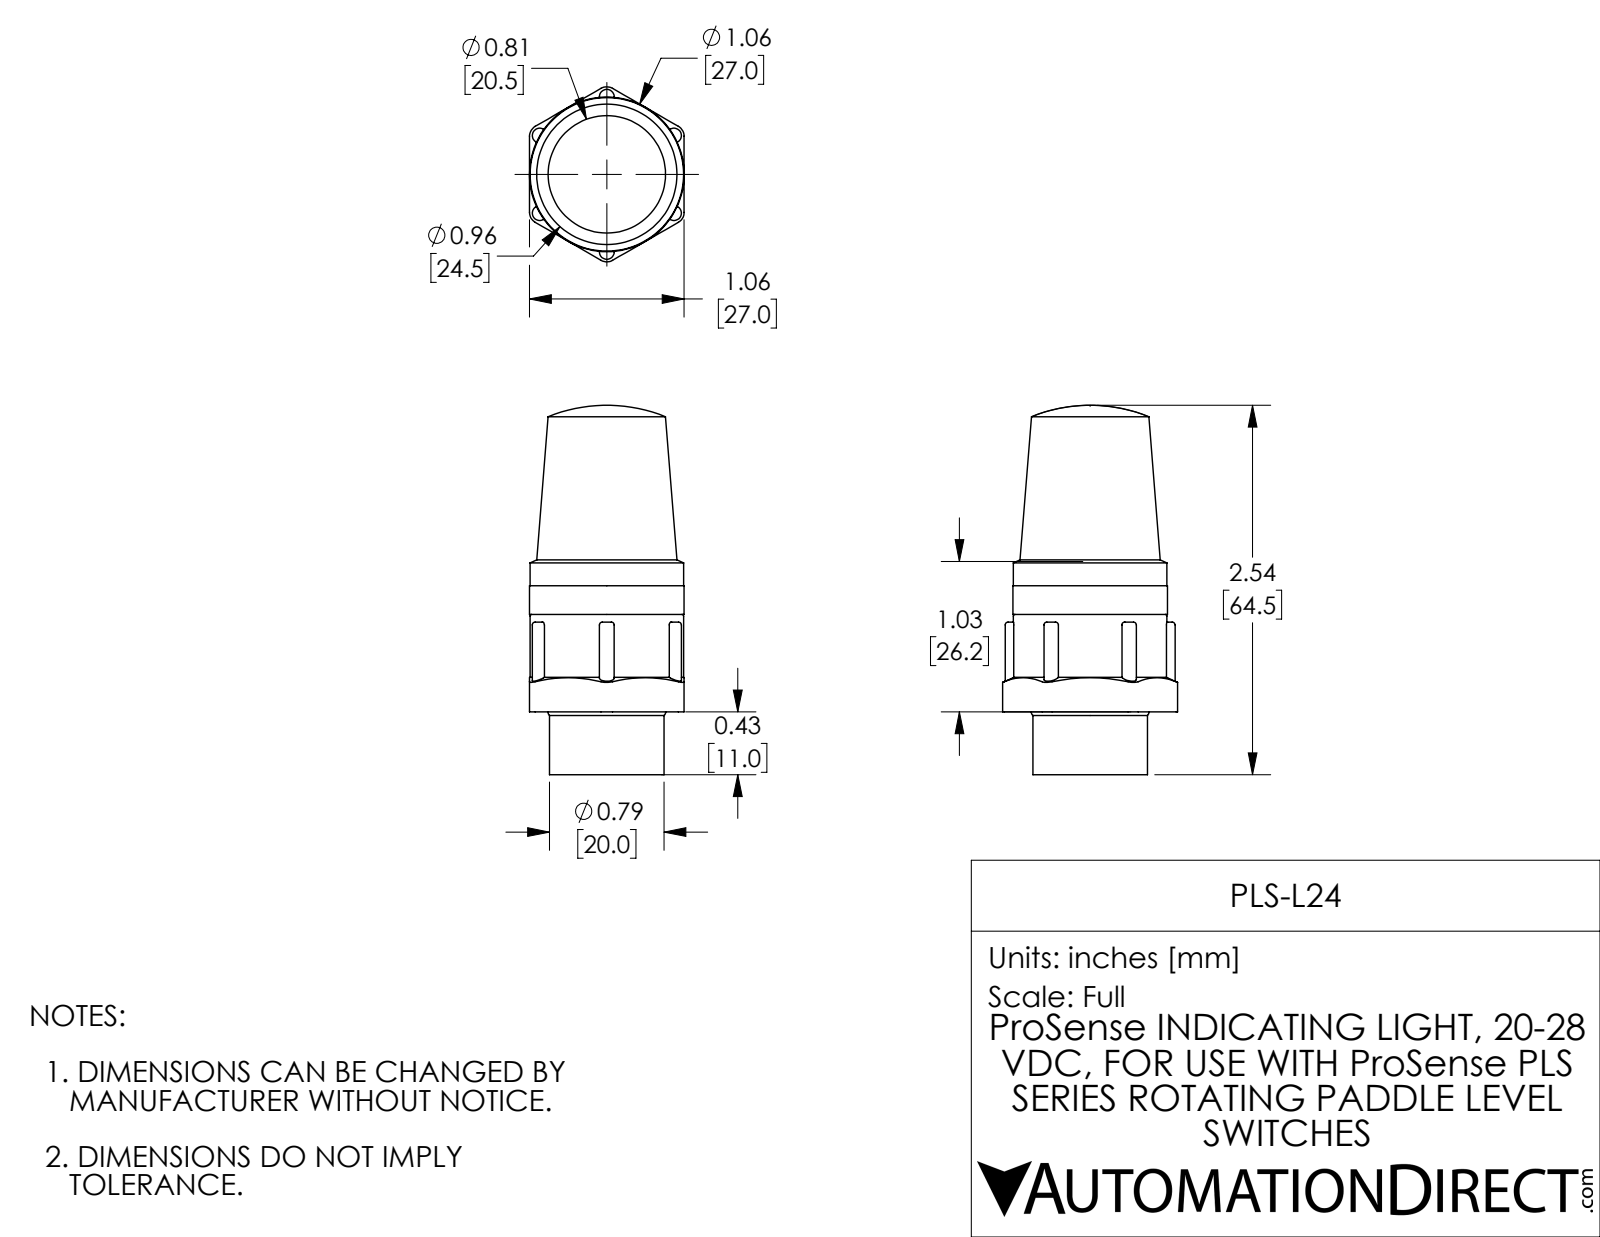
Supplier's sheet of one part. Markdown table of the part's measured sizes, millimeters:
| quantity | value |
| --- | --- |
| part name | Signal Light nc |
| STEP written by | SolidWorks 2017 (AUTOMOTIVE_DESIGN) |
| units | millimeters |
| bodies | 1 solid, 104 faces (40 planar, 43 cylindrical, 21 other) |
| overall size | 64.5 × 30.6 × 27 |
| volume | 24 940 mm³ |
| surface area | 8 568 mm² |
| round holes (diameter × count) | 1.2 × 2, 14.5 × 1, 21.3 × 1 |
| round bosses / shafts (diameter × count) | 27 × 1, 26.8 × 1, 20 × 1 |
| partial cylindrical surfaces (radius × count) | 0.5 × 6, 1.3 × 6, 2 × 6 |
| main face-to-face distances | 7, 27, 11, 18, 28, 17, 10, 2, 12.2, 14.8 |
| hole center spacings | 9 |
